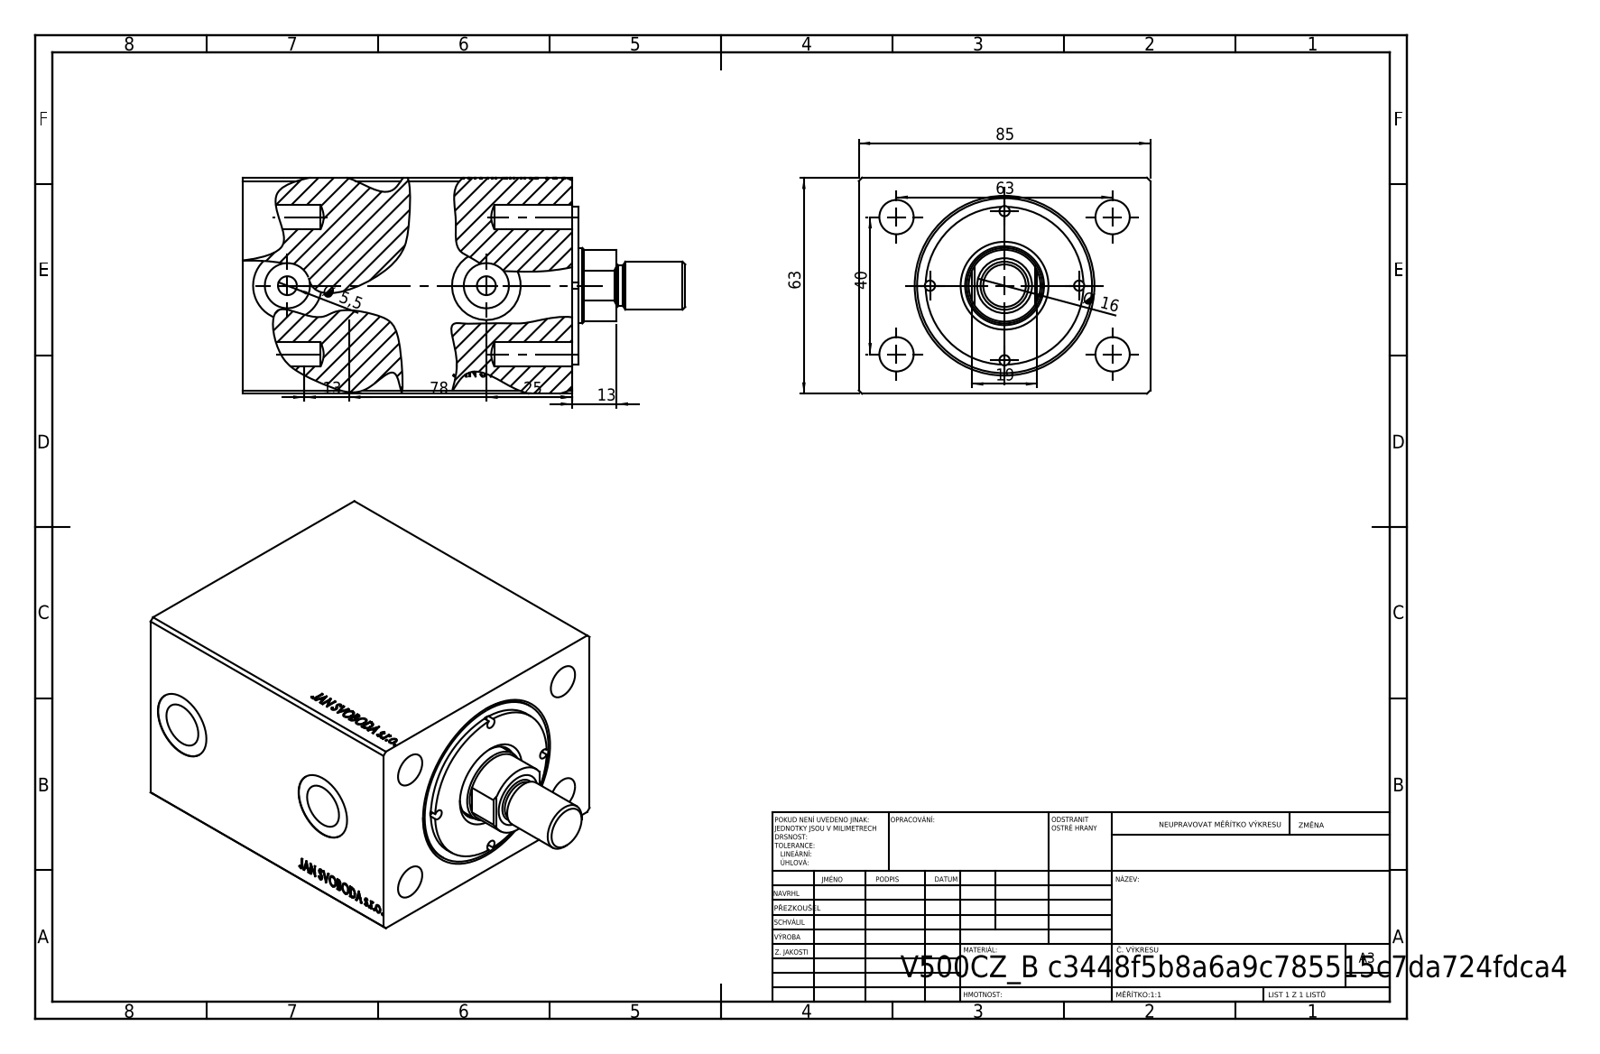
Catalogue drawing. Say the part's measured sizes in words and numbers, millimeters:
The part is named "V500CZ_FM; V500CZ; V500CZ_vnitrni_cast_vysunovaci". Its 3-D file was written by "SolidWorks 2019 (CONFIG_CONTROL_DESIGN)". It is 4 solids with 886 faces: 403 planar, 65 cylindrical and 418 other. Overall it measures 129 by 85 by 63 millimeters. Its volume is 478 160 cubic millimeters and its surface area 71 239 square millimeters. Round holes: 4 of diameter 3, 4 of diameter 10, 2 of diameter 5.5, 2 of diameter 13.16, 2 of diameter 20, 1 of diameter 16, 1 of diameter 22, 1 of diameter 23, 1 of diameter 36, 1 of diameter 40, 1 of diameter 51. Round bosses or shafts: 1 of diameter 46, 1 of diameter 14, 1 of diameter 12. Partial cylindrical surfaces (rounded edges, fillets, slot ends): 1 of radius 10.46. The main face-to-face distances are 63, 85, 96, 60, 36, 10, 50, 86, 25, 1.8. The hole center spacings are 21.75, 22.25, 30.76, 31.55, 37.31, 52.3, 56.88, 40.
